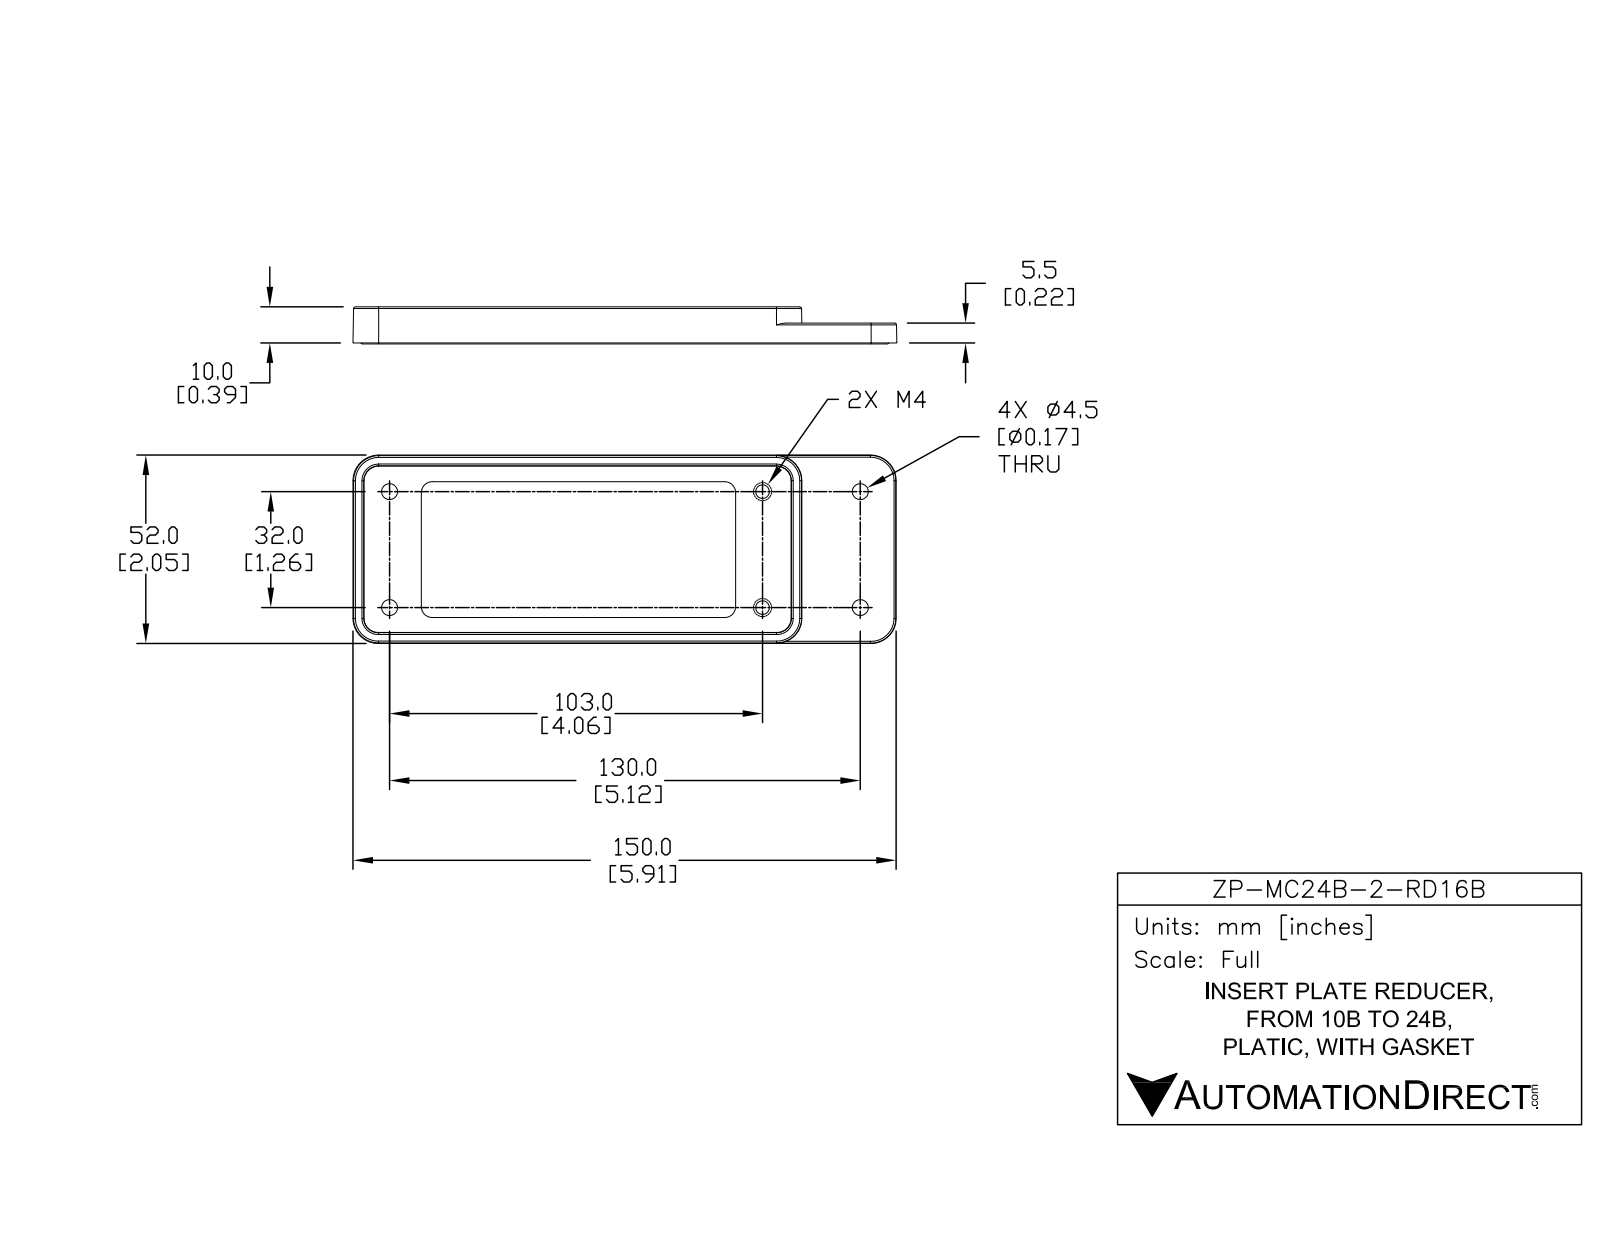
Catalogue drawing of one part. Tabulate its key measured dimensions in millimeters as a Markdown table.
| quantity | value |
| --- | --- |
| part name | ZP-MC24B-2-RD16B |
| STEP written by | SolidWorks 2014 (AUTOMOTIVE_DESIGN) |
| units | millimeters |
| bodies | 1 solid, 169 faces (65 planar, 76 cylindrical, 28 other) |
| overall size | 150.19 × 52.19 × 10.25 |
| volume | 25 173 mm³ |
| surface area | 16 508 mm² |
| round holes (diameter × count) | 3.75 × 4, 4.4 × 4 |
| partial cylindrical surfaces (radius × count) | 0.5 × 27, 1.5 × 4, 3 × 4, 4.2 × 4, 1.5 × 2, 1.52 × 2, 5.5 × 2 |
| main face-to-face distances | 5.5, 3, 2.5, 49.05, 3.25, 5.75, 10.25, 10, 7, 4.5 |
| hole center spacings | 27, 103, 32, 31.98, 41.85, 41.87, 107.85, 107.86 |
